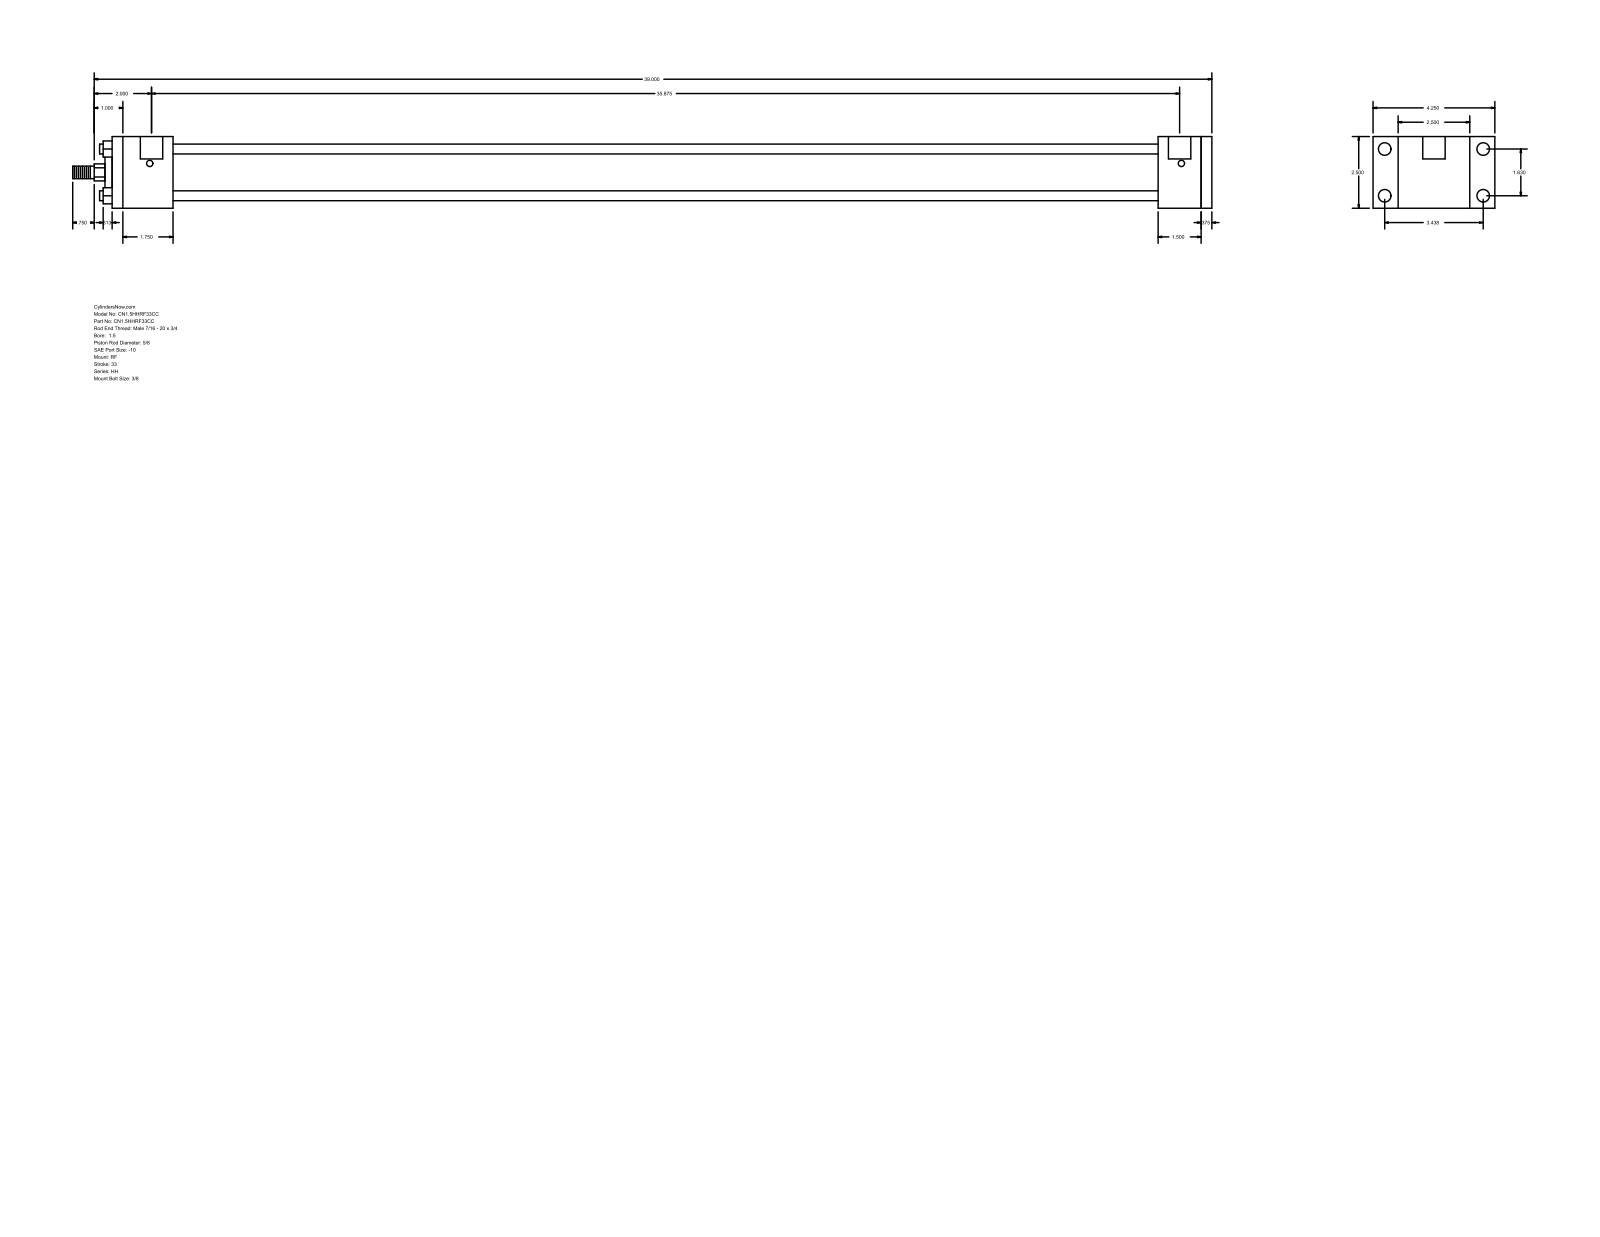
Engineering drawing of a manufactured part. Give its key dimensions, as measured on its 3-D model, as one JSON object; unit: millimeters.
{"part_name": "HH_RF__0150_0.625", "step_written_by": "GSSL Pune (CONFIG_CONTROL_DESIGN)", "units": "millimeters", "bodies": {"solids": 0, "faces": 92, "planar": 64, "cylindrical": 28, "other": 0}, "overall_size": [1009.65, 107.95, 63.5], "round_holes": [[5.56, 4], [11.13, 4], [19.84, 2]], "round_bosses_or_shafts": [[8.76, 4], [44.45, 1], [28.57, 1], [15.88, 1], [11.11, 1]], "partial_cylinders_radius": [[7.54, 1]], "face_to_face_distances": [63.5, 974.72, 38.1, 965.2, 9.52, 53.97, 927.1, 873.13, 911.23, 920.75], "hole_center_spacings": [1.59, 41.4, 87.32, 96.64, 912.81, 914.4, 911.22]}
